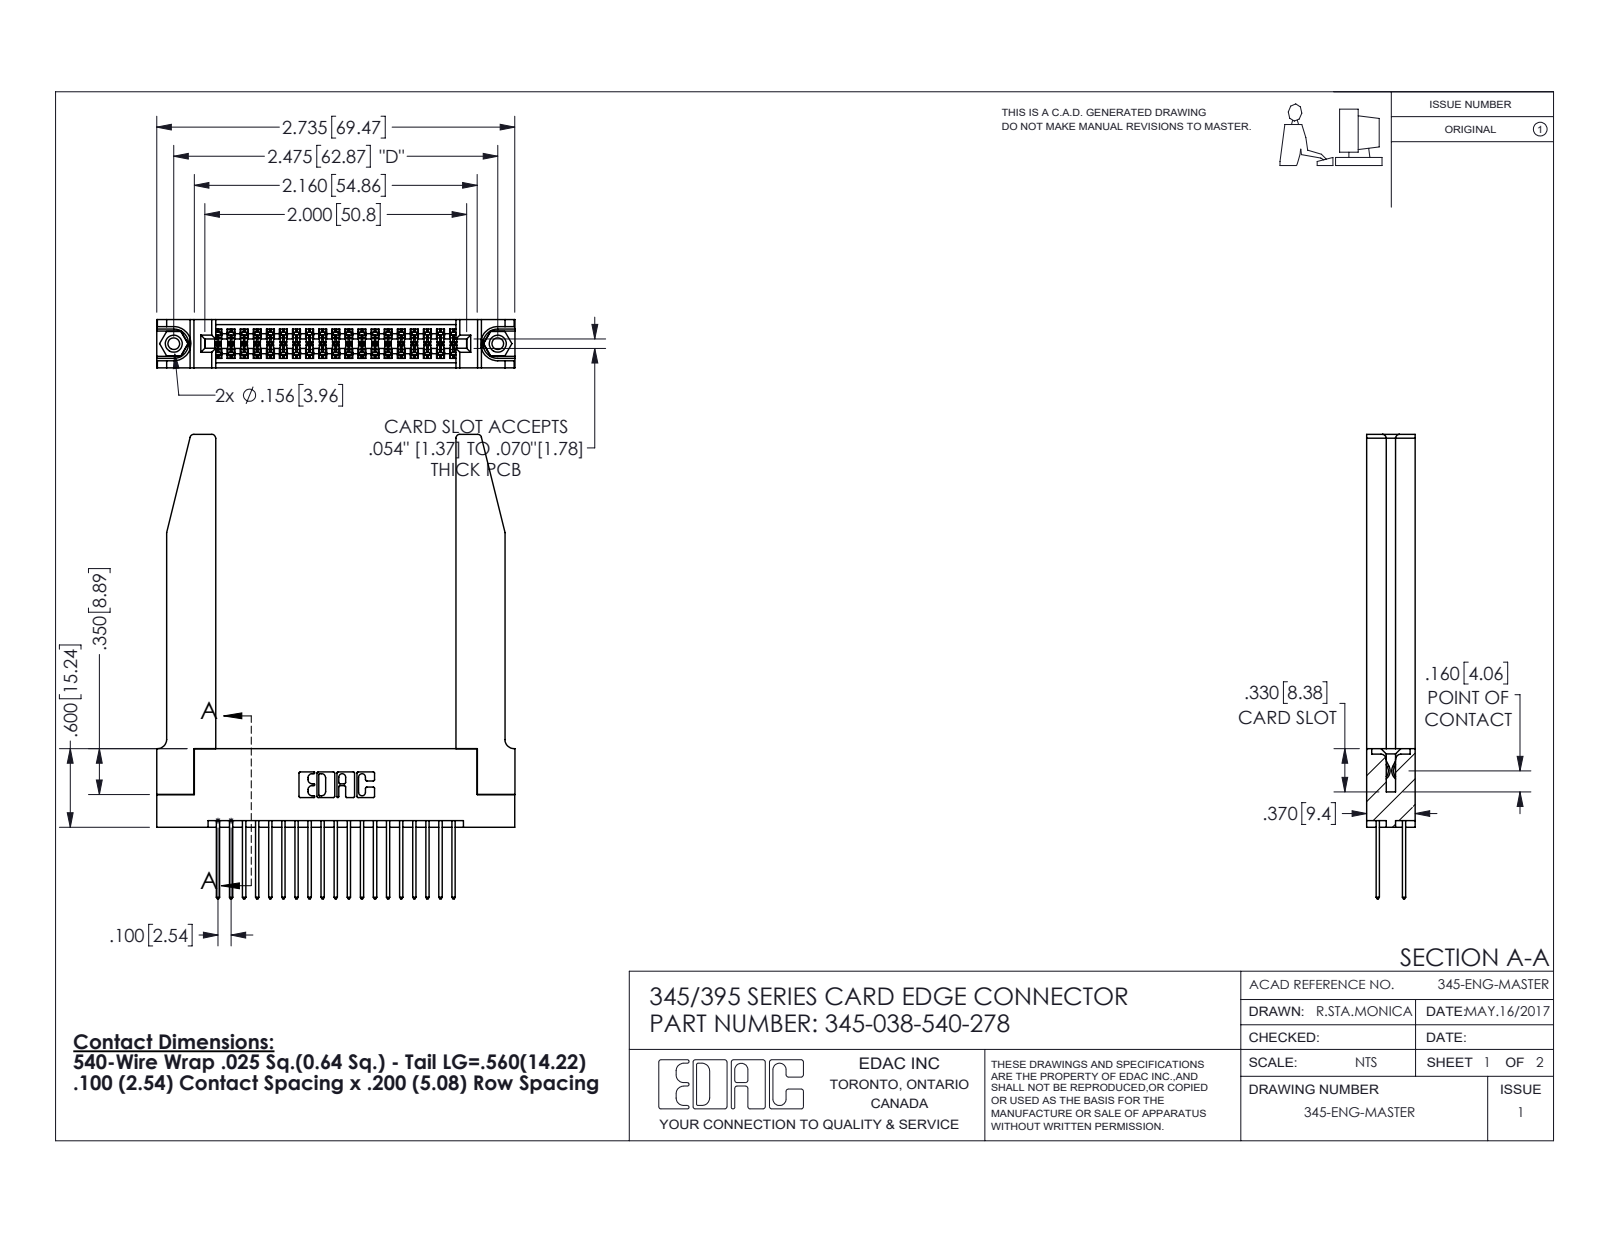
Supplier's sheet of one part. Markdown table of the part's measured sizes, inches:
| quantity | value |
| --- | --- |
| part name | 345-038-540-278; 345 Part_Flush Mounting Lugs - 0.156 Dia-TH; 345-220-078_345-220-078; 345-292-001_345-293-140 (+1 more) |
| STEP written by | SolidWorks 2016 (CONFIG_CONTROL_DESIGN) |
| units | inches |
| bodies | 43 solids, 2260 faces (1476 planar, 732 cylindrical, 52 other) |
| overall size | 3.547 × 2.736 × 0.37 |
| volume | 0.882 in³ |
| surface area | 26.25 in² |
| round holes (diameter × count) | 0.089 × 2, 0.125 × 2, 0.156 × 2, 0.064 × 1 |
| round bosses / shafts (diameter × count) | 0.155 × 2 |
| partial cylindrical surfaces (radius × count) | 0.006 × 57, 0.01 × 38, 0.01 × 22, 0.03 × 8, 0.007 × 6, 0.031 × 6, 0.026 × 3, 0.014 × 2 |
| main face-to-face distances | 0.37, 0.072, 0.298, 0.2, 0.098, 0.272, 0.025, 0.225, 0.148, 0.15 |
| hole center spacings | 0.27, 2.241, 2.475 |
